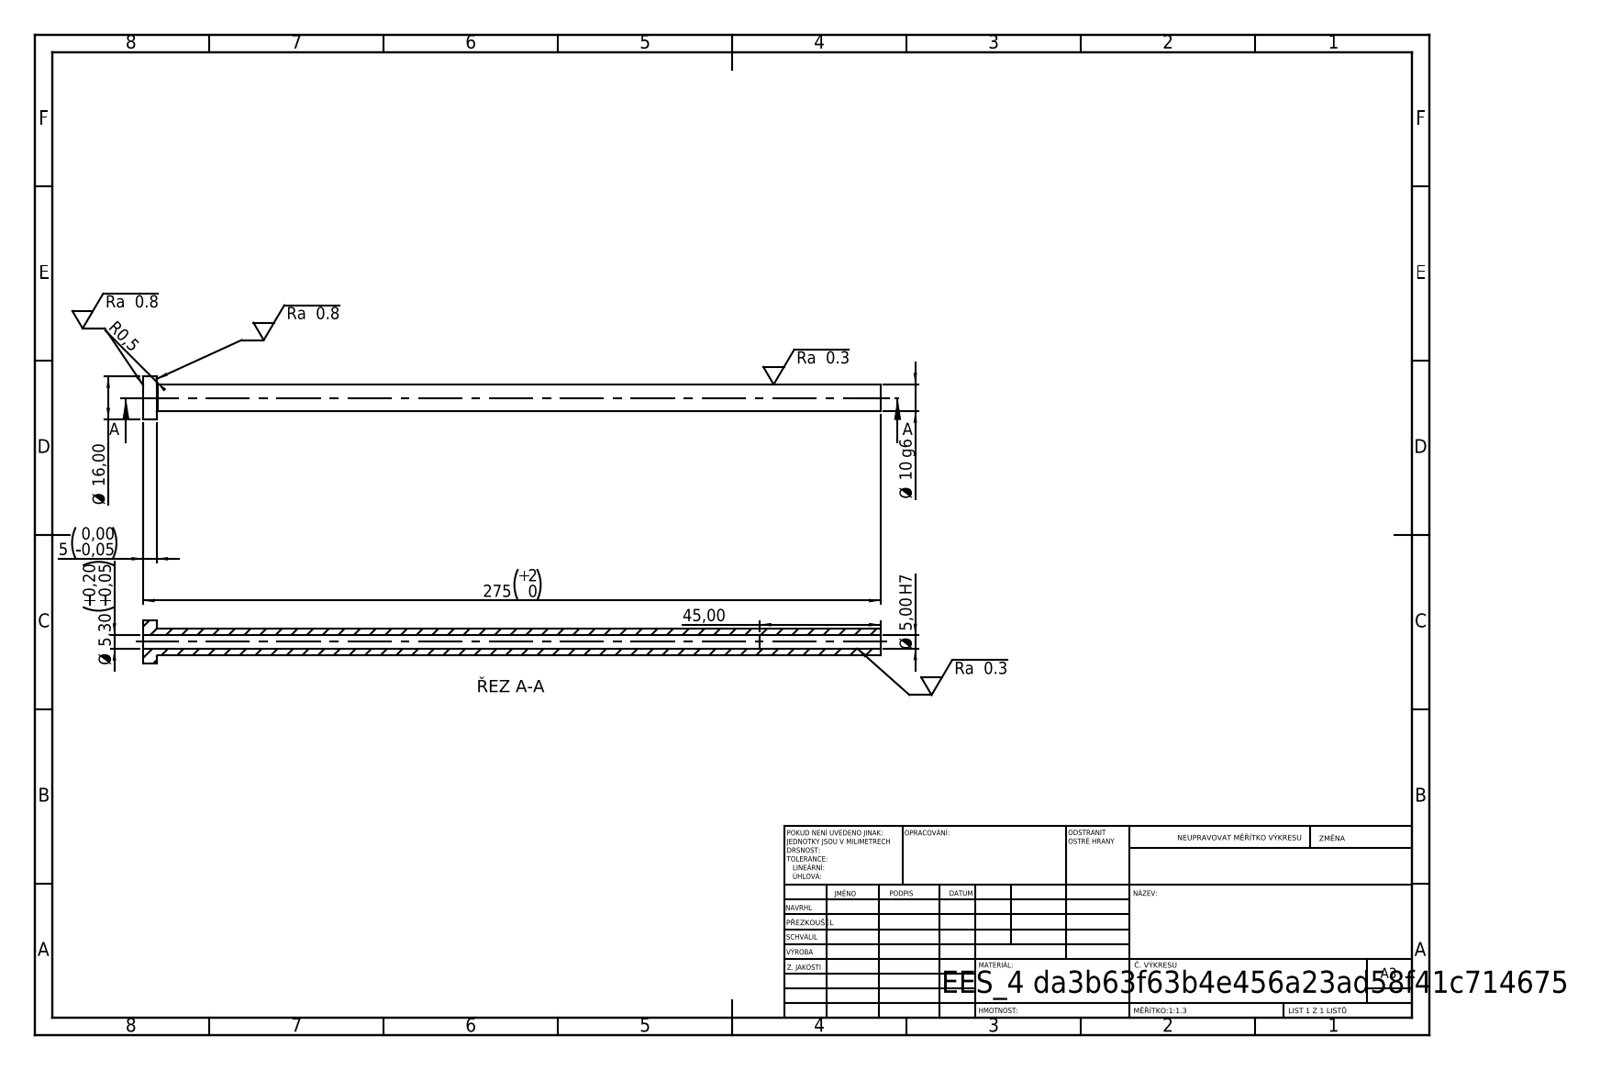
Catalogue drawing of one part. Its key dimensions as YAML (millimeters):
step_written_by: "SolidWorks 2019 (CONFIG_CONTROL_DESIGN)"
units: millimeters
bodies: {solids: 1, faces: 14, planar: 4, cylindrical: 8, other: 2}
overall_size: [275, 16, 16]
volume: 16255
surface_area: 13626
round_holes:
  - {diameter: 5, count: 1}
  - {diameter: 5.3, count: 1}
round_bosses_or_shafts:
  - {diameter: 16, count: 1}
  - {diameter: 10, count: 1}
face_to_face_distances: [5, 275, 270, 230, 225, 45]
